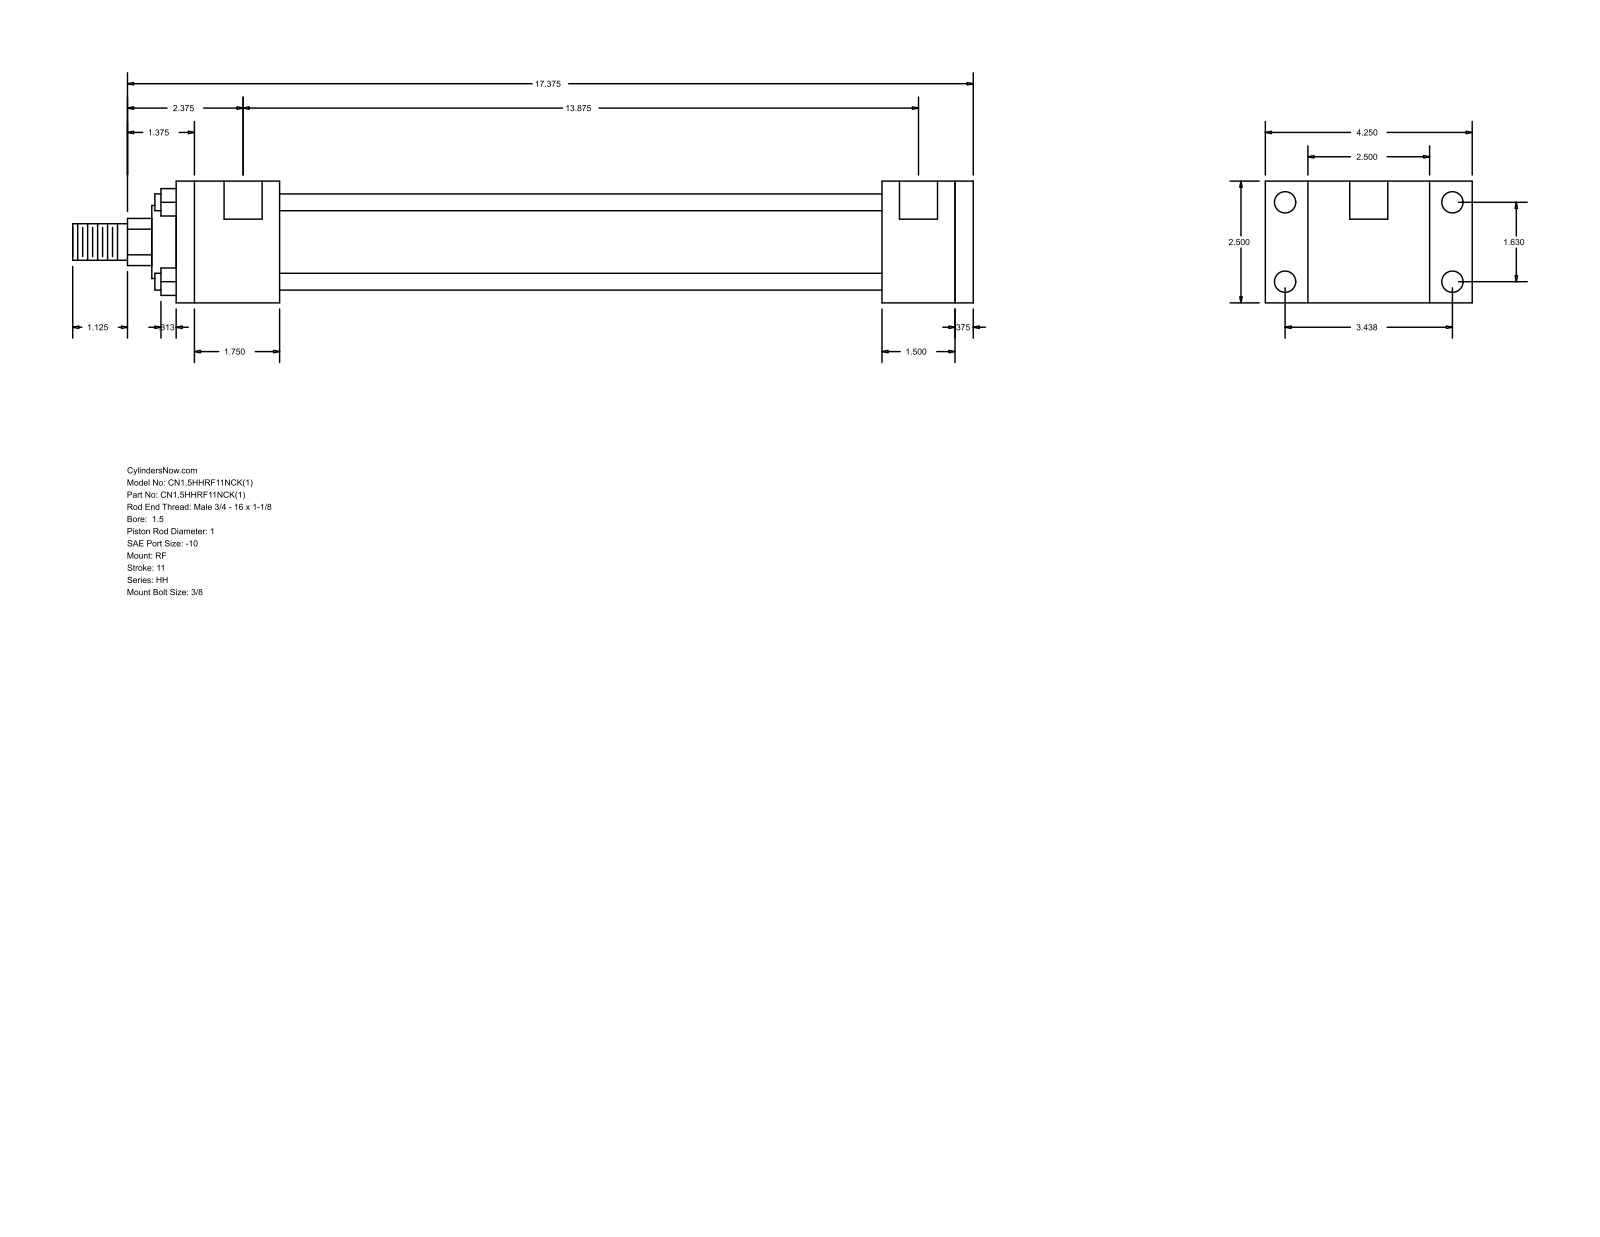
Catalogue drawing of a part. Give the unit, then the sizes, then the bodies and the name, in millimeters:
Units: millimetres
Overall size (bounding box): 469.9 × 107.95 × 63.5
Round holes (diameter × count): ⌀5.56 ×4, ⌀11.13 ×4, ⌀19.84 ×2
Round bosses / shafts (diameter × count): ⌀8.76 ×4, ⌀44.45 ×1, ⌀38.1 ×1, ⌀25.4 ×1, ⌀19.05 ×1
Partial cylindrical surfaces — rounded edges, fillets, slot ends (radius × count): R12.29 ×1
Main face-to-face distances: 63.5, 9.52, 38.1, 314.32, 352.42, 361.94, 47.62, 53.98, 368.3, 406.4
Hole centre spacings: 1.59, 41.4, 87.32, 96.64, 354.01, 355.6, 352.42
Bodies: 0 solids, 92 faces (64 planar, 28 cylindrical, 0 other)
Part name (STEP PRODUCT): HH_RF__0150_1
STEP written by: GSSL Pune (CONFIG_CONTROL_DESIGN)
